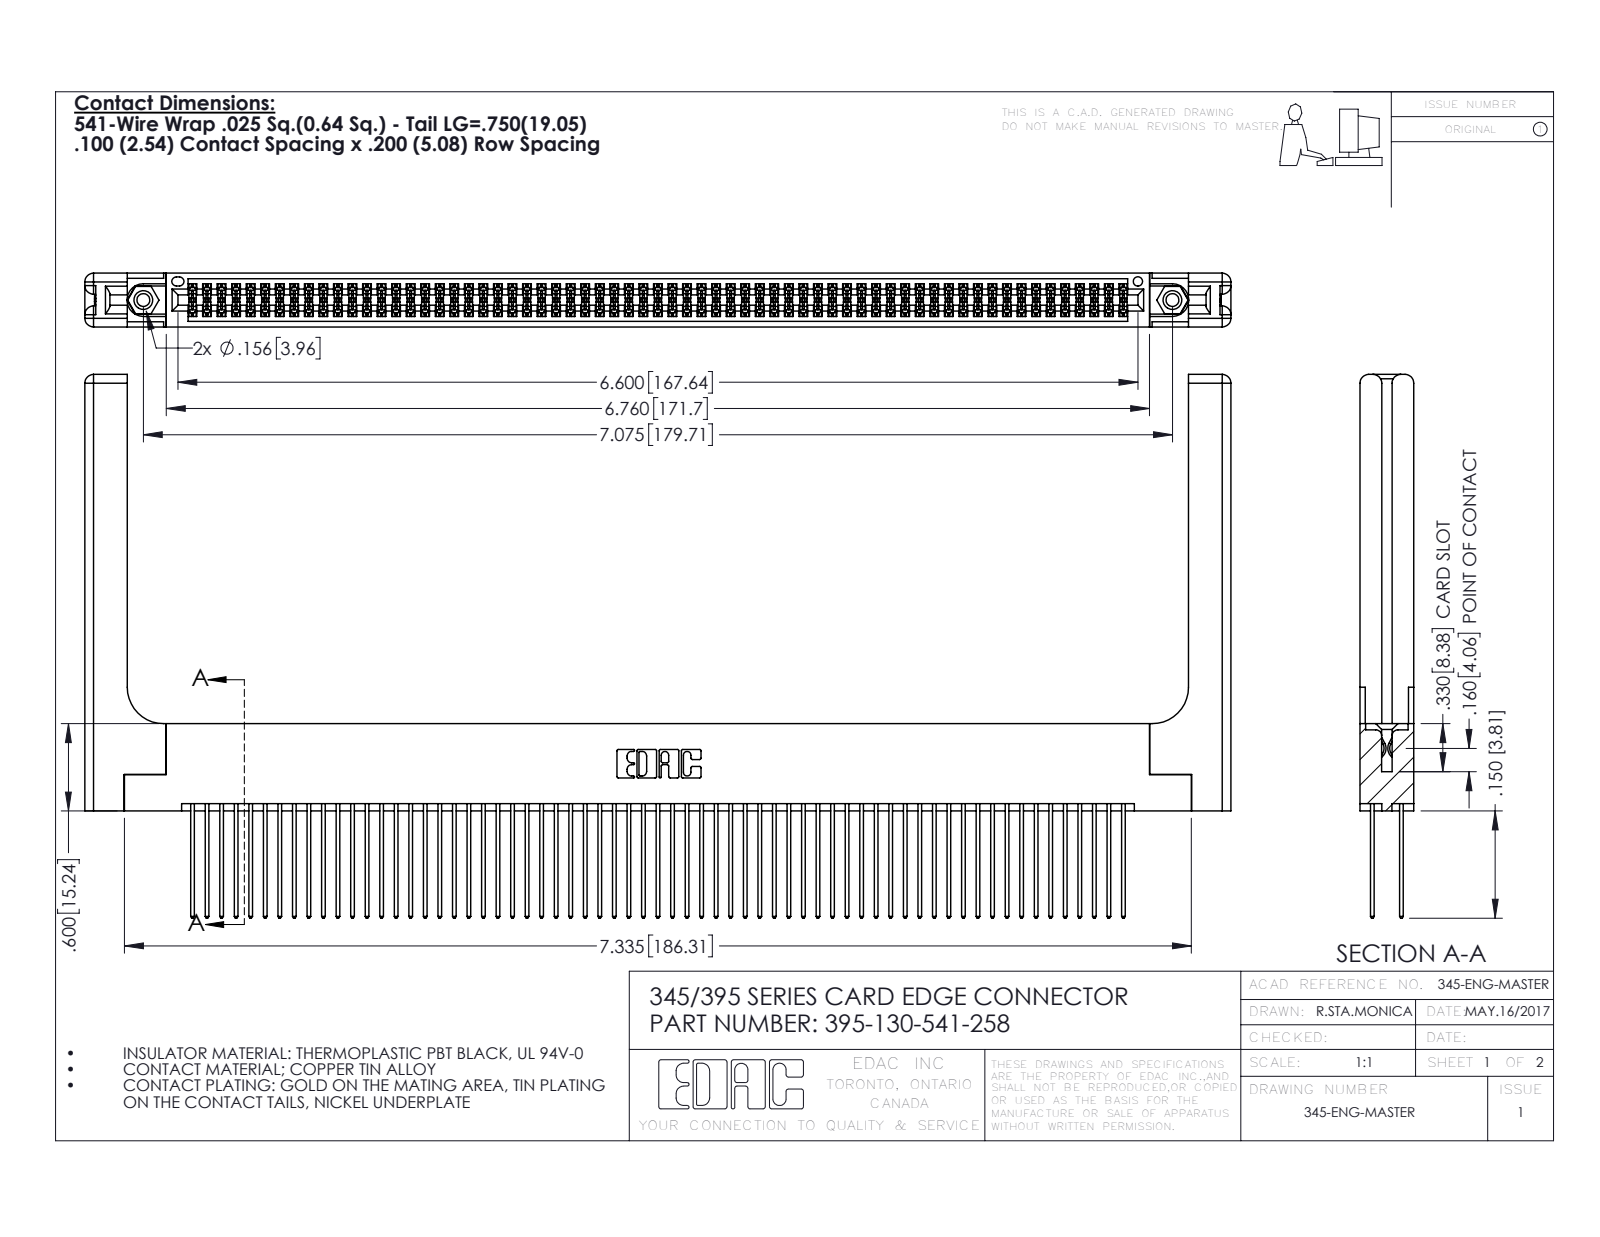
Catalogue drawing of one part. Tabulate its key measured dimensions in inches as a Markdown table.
| quantity | value |
| --- | --- |
| part name | 345-250-001_345-250-001-102; 345 Part_Flush Mounting Lugs - 0.156 Dia-TH; 345-220-058_345-220-058; 395-130-541-258 (+1 more) |
| STEP written by | SolidWorks 2016 (CONFIG_CONTROL_DESIGN) |
| units | inches |
| bodies | 135 solids, 6882 faces (4518 planar, 2304 cylindrical, 60 other) |
| overall size | 7.879 × 3.737 × 0.37 |
| volume | 1.762 in³ |
| surface area | 60.71 in² |
| round holes (diameter × count) | 0.089 × 2, 0.125 × 2, 0.156 × 2, 0.064 × 1 |
| round bosses / shafts (diameter × count) | 0.155 × 2 |
| partial cylindrical surfaces (radius × count) | 0.006 × 195, 0.01 × 130, 0.01 × 22, 0.06 × 16, 0.007 × 6, 0.031 × 6, 0.026 × 3, 0.014 × 2 |
| main face-to-face distances | 0.072, 0.298, 0.2, 0.098, 0.272, 0.025, 0.37, 0.225, 0.175, 0.148 |
| hole center spacings | 0.27, 6.839, 7.075 |
